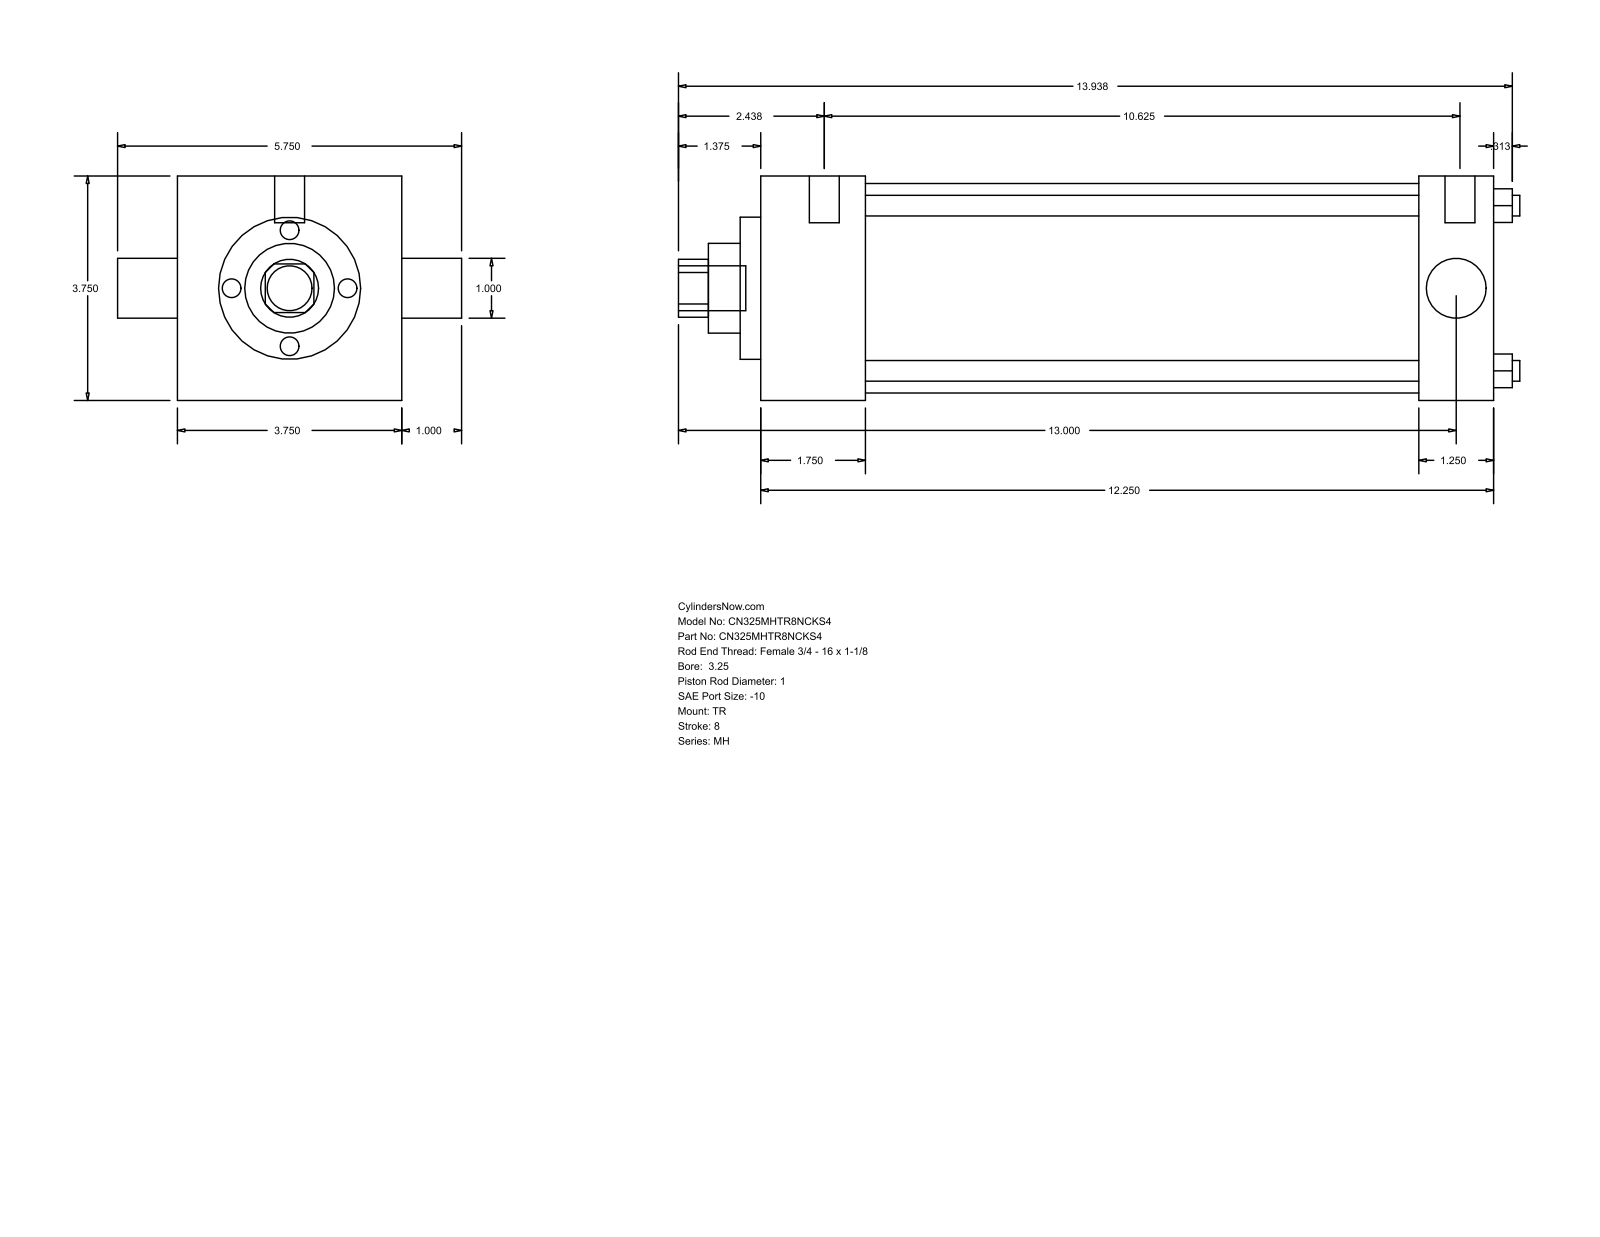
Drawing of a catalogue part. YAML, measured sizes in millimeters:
part_name: "MH_TR__0325_1"
step_written_by: "GSSL Pune (CONFIG_CONTROL_DESIGN)"
units: millimeters
bodies: {solids: 0, faces: 86, planar: 61, cylindrical: 25, other: 0}
overall_size: [357.19, 146.05, 95.25]
round_holes:
  - {diameter: 8.76, count: 4}
  - {diameter: 25.4, count: 2}
  - {diameter: 38.1, count: 1}
  - {diameter: 60.33, count: 1}
  - {diameter: 88.9, count: 1}
round_bosses_or_shafts:
  - {diameter: 5.56, count: 3}
  - {diameter: 12.7, count: 2}
  - {diameter: 19.05, count: 1}
partial_cylinders:
  - {radius: 12.29, count: 1}
face_to_face_distances: [95.24, 311.15, 44.46, 279.4, 234.94, 266.69, 31.75, 8.73, 53.19, 288.13]
hole_center_spacings: [49.57, 70.1, 99.14]
